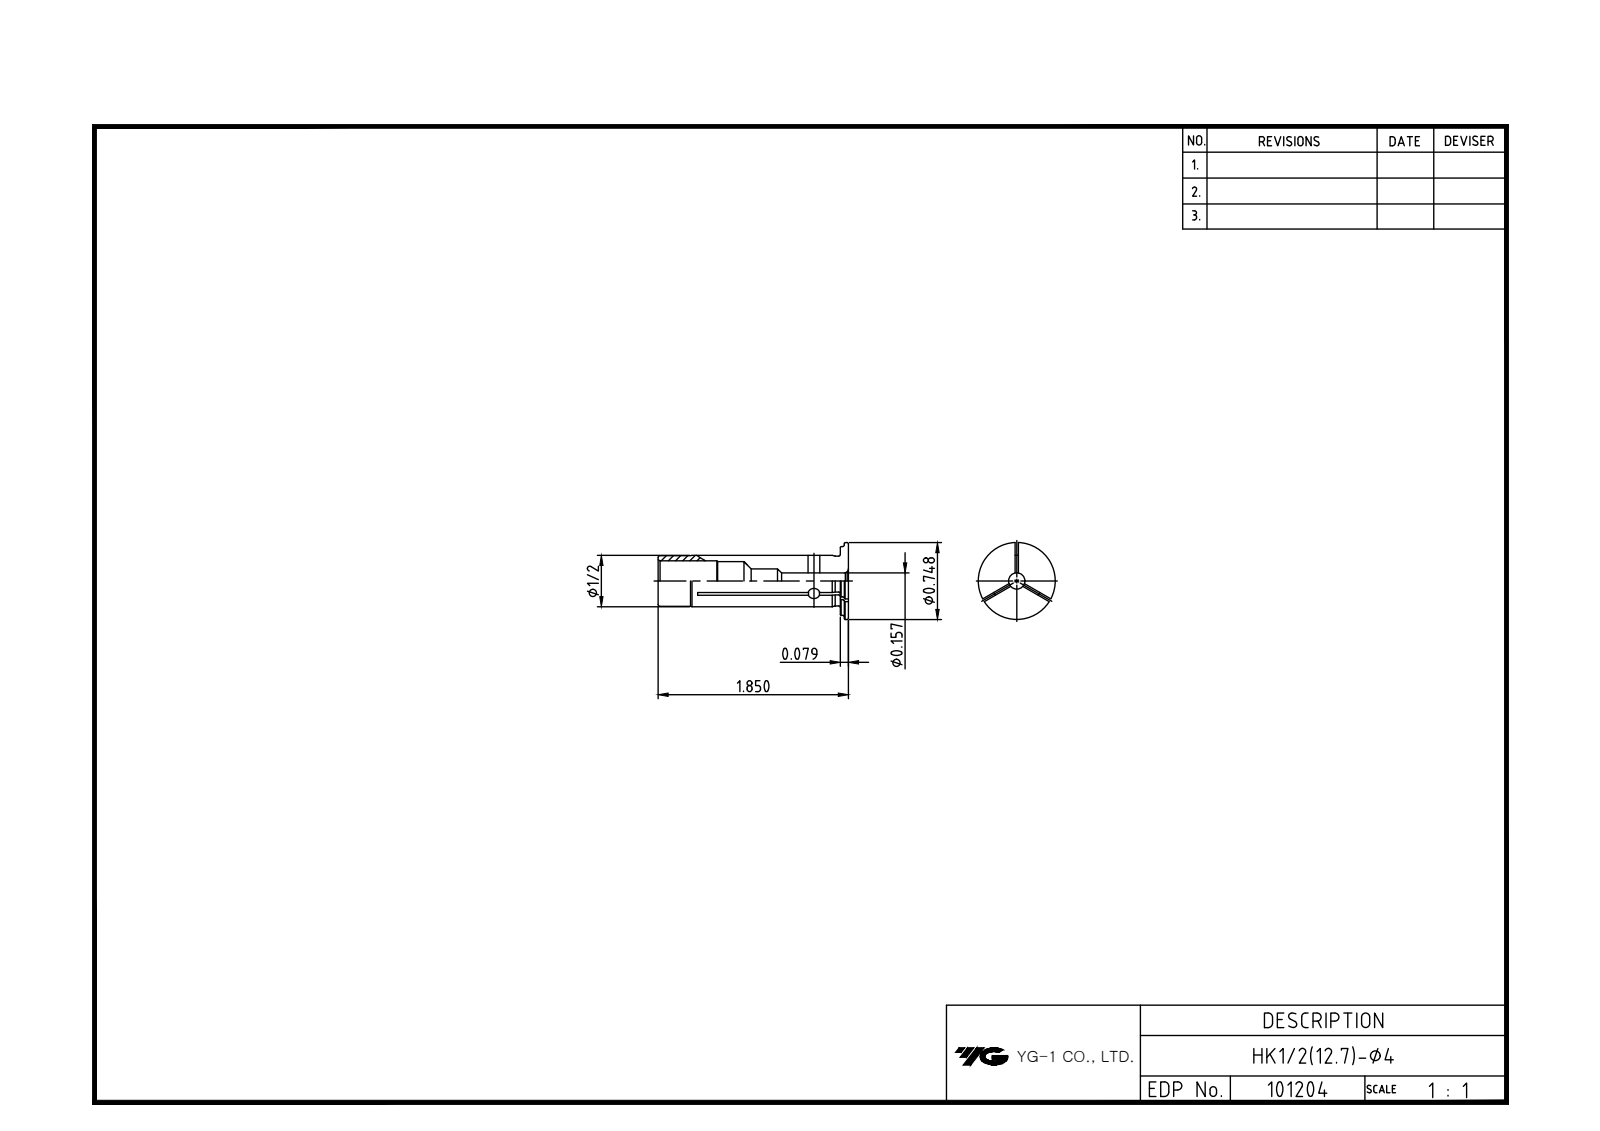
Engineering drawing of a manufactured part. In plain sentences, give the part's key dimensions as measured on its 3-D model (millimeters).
The part is named "LO-HK12.7-4". Its 3-D file was written by "Autodesk Inventor 2025 (AP242_MANAGED_MODEL_BASED_3D_ENGINEERING_MIM_LF)". It is 1 solid with 14 faces: 4 planar, 7 cylindrical and 3 other. Overall it measures 47 by 19 by 19 millimeters. Its volume is 4 088 cubic millimeters and its surface area 3 459 square millimeters. Round holes: 1 of diameter 4, 1 of diameter 6, 1 of diameter 9.6, 1 of diameter 10. Round bosses or shafts: 1 of diameter 19, 1 of diameter 17, 1 of diameter 12.7. The main face-to-face distances are 1, 2, 45, 46, 47.
